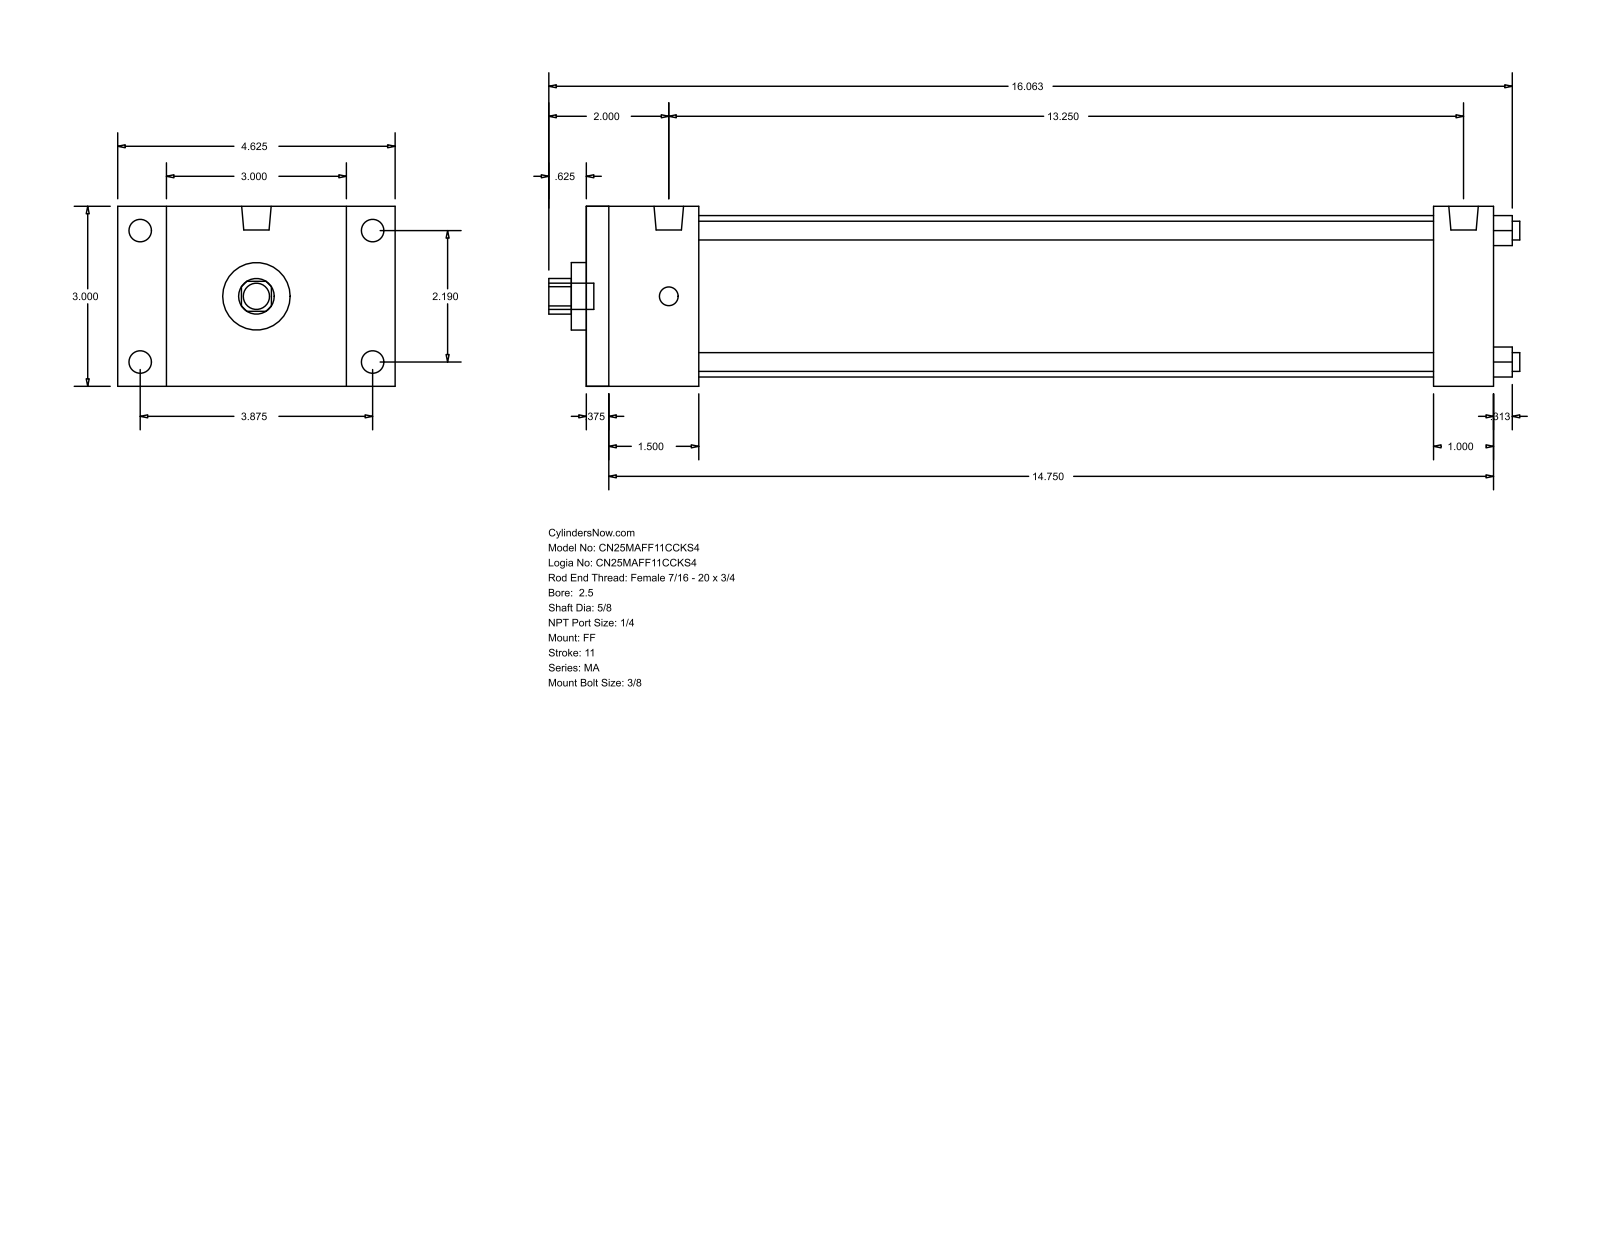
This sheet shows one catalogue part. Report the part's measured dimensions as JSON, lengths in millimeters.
{"part_name": "MA_FF__0250_0.625", "step_written_by": "GSSL Pune (CONFIG_CONTROL_DESIGN)", "units": "millimeters", "bodies": {"solids": 0, "faces": 92, "planar": 64, "cylindrical": 28, "other": 0}, "overall_size": [411.16, 117.47, 76.2], "round_holes": [[7.94, 4], [15.88, 1], [28.57, 1], [68.33, 1]], "round_bosses_or_shafts": [[9.53, 4], [7.94, 4], [12.49, 2], [11.11, 1]], "partial_cylinders_radius": [[7.54, 1]], "face_to_face_distances": [76.2, 384.17, 9.52, 374.65, 25.4, 47.62, 358.77, 38.1, 349.25, 311.15], "hole_center_spacings": [39.33, 55.62, 78.66]}
